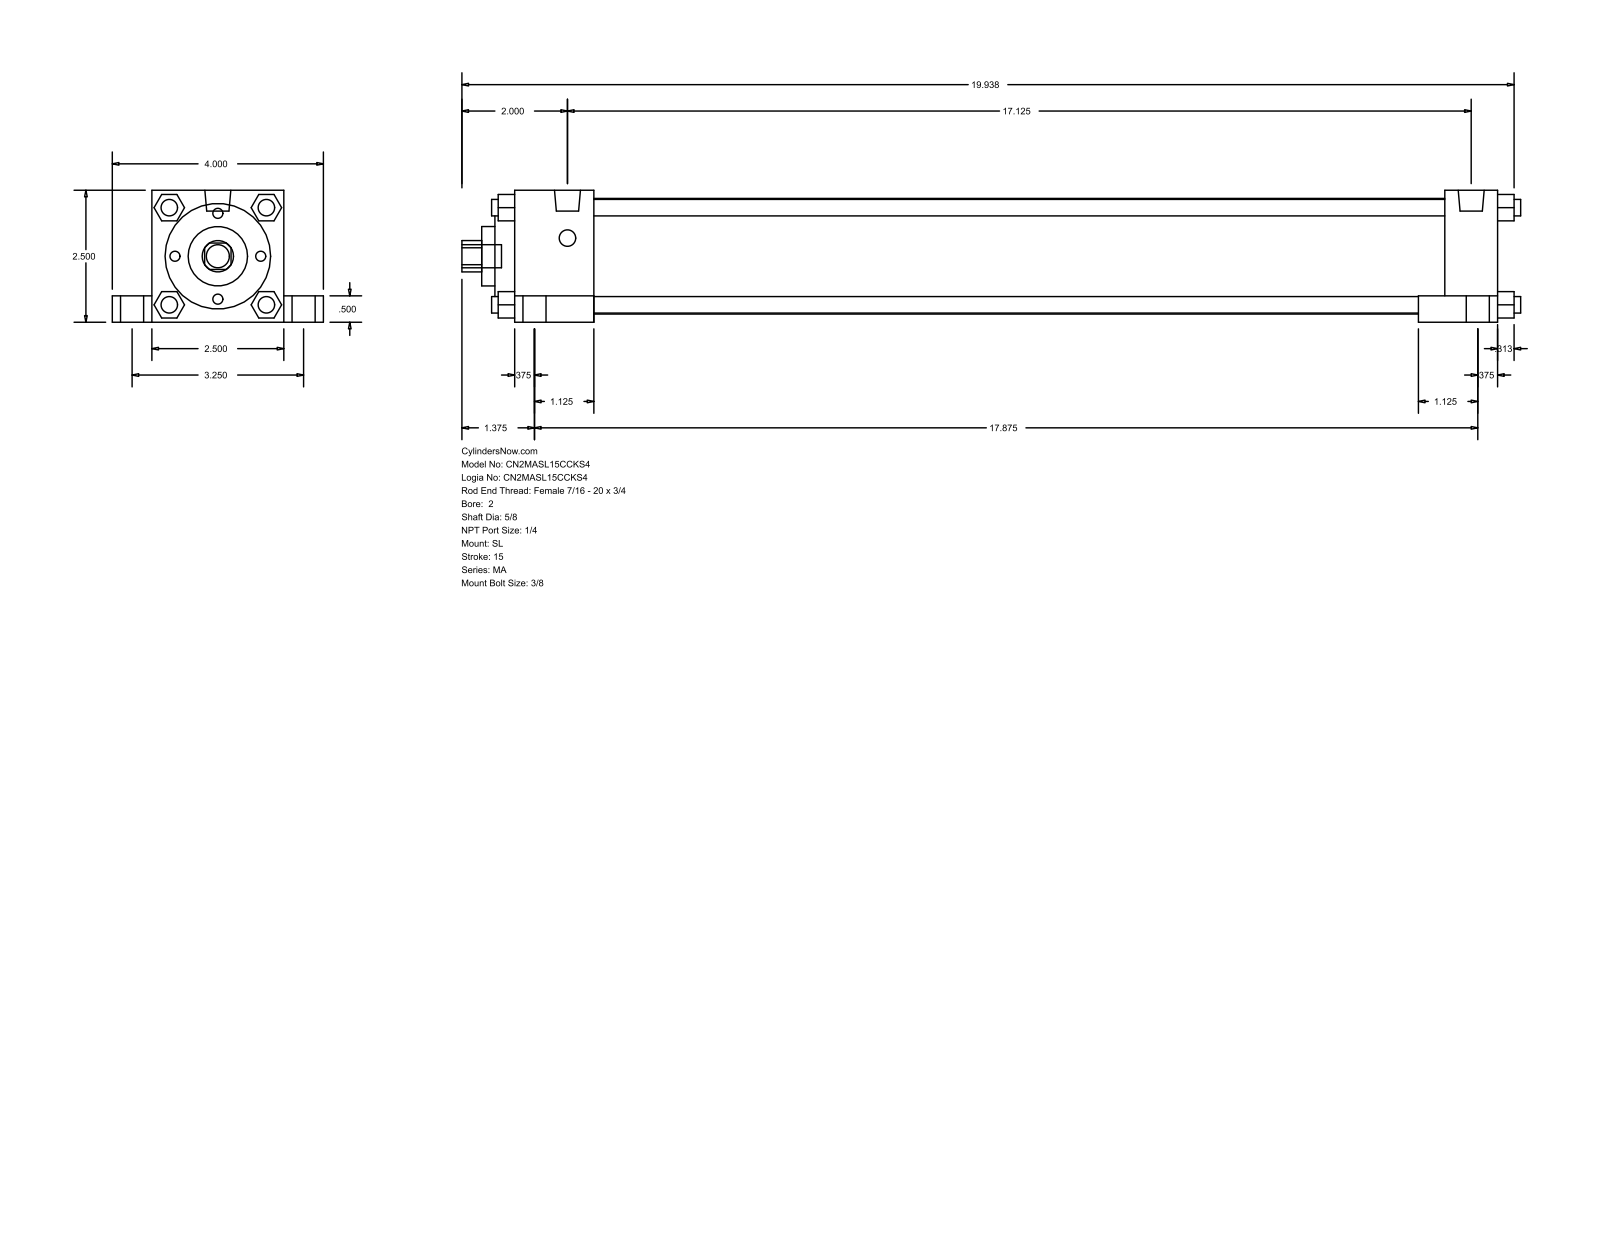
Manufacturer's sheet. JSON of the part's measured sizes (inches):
{"part_name": "MA_SL__0200_0.625", "step_written_by": "GSSL Pune (CONFIG_CONTROL_DESIGN)", "units": "inches", "bodies": {"solids": 0, "faces": 150, "planar": 113, "cylindrical": 37, "other": 0}, "overall_size": [20.063, 4, 2.5], "round_holes": [[0.625, 1], [1.125, 1], [2, 1], [2.19, 1]], "round_bosses_or_shafts": [[0.313, 8], [0.437, 5], [0.687, 4], [0.492, 2]], "partial_cylinders_radius": [[0.297, 1]], "face_to_face_distances": [2.5, 0.5, 0.375, 16.125, 0.75, 3.25, 1.5, 2, 18.625, 17.125]}
